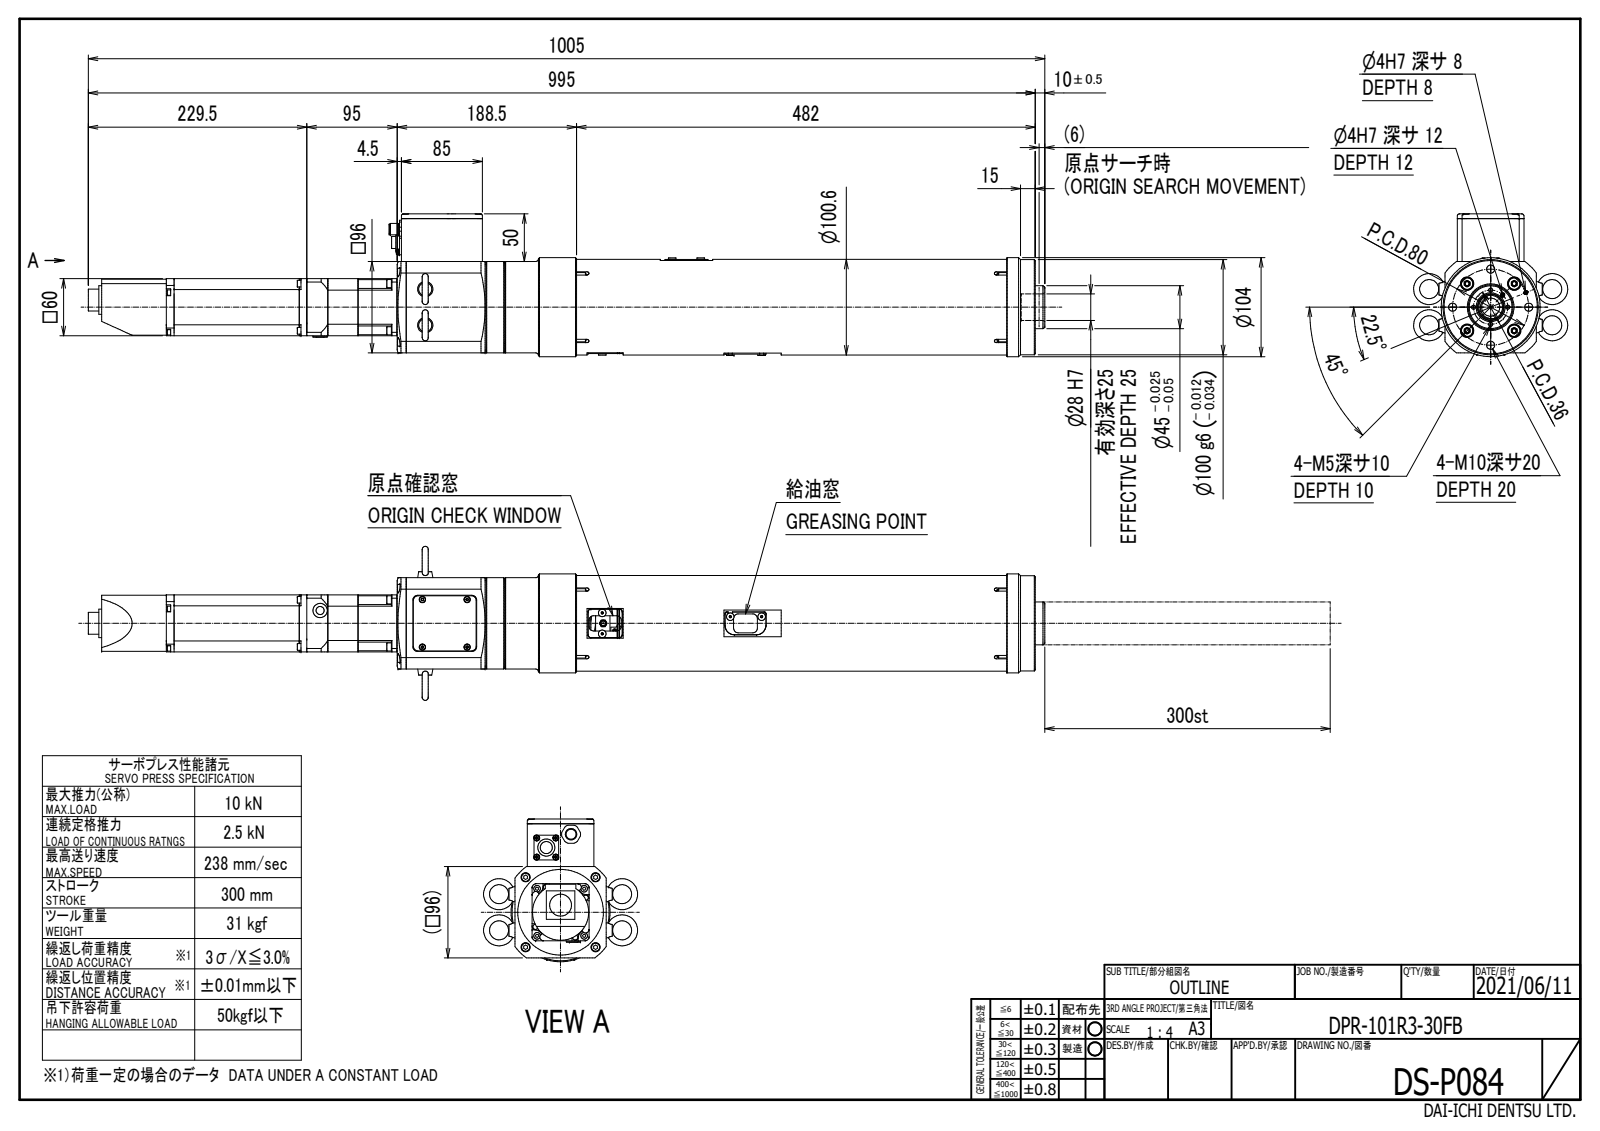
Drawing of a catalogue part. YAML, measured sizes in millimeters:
part_name: "DPR-101R3-30FB(DS-P084)"
step_written_by: "Autodesk Inventor 2021 (AUTOMOTIVE_DESIGN)"
units: millimeters
bodies: {solids: 1, faces: 1364, planar: 734, cylindrical: 363, other: 267}
overall_size: [1005, 161.9, 150]
volume: 6626000
surface_area: 367969
round_holes:
  - {diameter: 2.46, count: 4}
  - {diameter: 3.1, count: 4}
  - {diameter: 3.2, count: 4}
  - {diameter: 3.3, count: 4}
  - {diameter: 3.4, count: 4}
  - {diameter: 4.2, count: 4}
  - {diameter: 4.92, count: 4}
  - {diameter: 8, count: 4}
  - {diameter: 8.5, count: 4}
  - {diameter: 9, count: 4}
  - {diameter: 9.5, count: 4}
  - {diameter: 14, count: 4}
round_bosses_or_shafts:
  - {diameter: 8.5, count: 12}
  - {diameter: 6, count: 8}
  - {diameter: 8, count: 6}
  - {diameter: 13, count: 4}
  - {diameter: 7, count: 4}
  - {diameter: 5.9, count: 4}
  - {diameter: 5.5, count: 4}
  - {diameter: 5, count: 4}
partial_cylinders:
  - {radius: 5, count: 35}
  - {radius: 0.2, count: 20}
  - {radius: 2, count: 14}
  - {radius: 4.5, count: 8}
  - {radius: 0.5, count: 4}
  - {radius: 2.5, count: 4}
  - {radius: 3, count: 4}
  - {radius: 3.25, count: 4}
face_to_face_distances: [60, 18, 78, 11.5, 48.5, 0.5, 66.5, 29.5, 96, 77.5]
hole_center_spacings: [25.65, 29.07, 36.91, 41.28, 43.86, 49.4, 62.68, 64.96]
